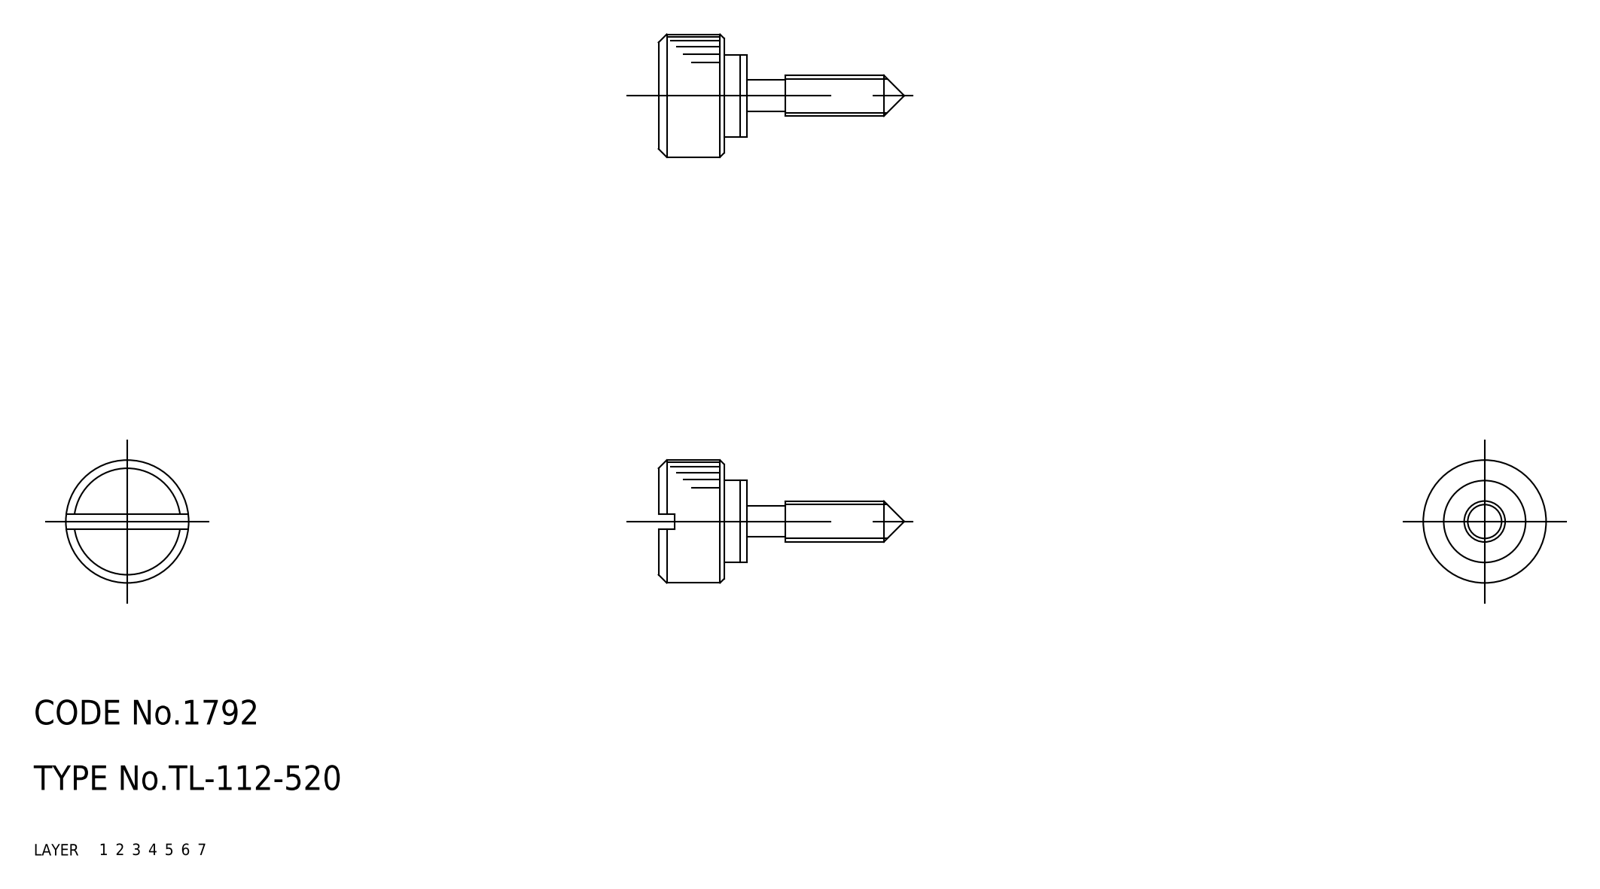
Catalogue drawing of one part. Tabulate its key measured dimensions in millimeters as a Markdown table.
| quantity | value |
| --- | --- |
| part name | washer; knob; TL_112_520_8602_36 |
| STEP written by | CADfix (AUTOMOTIVE_DESIGN) |
| units | millimeters |
| bodies | 2 solids, 42 faces (0 planar, 0 cylindrical, 42 other) |
| overall size | 30 × 15 × 15 |
| volume | 1 857 mm³ |
| surface area | 1 244 mm² |
